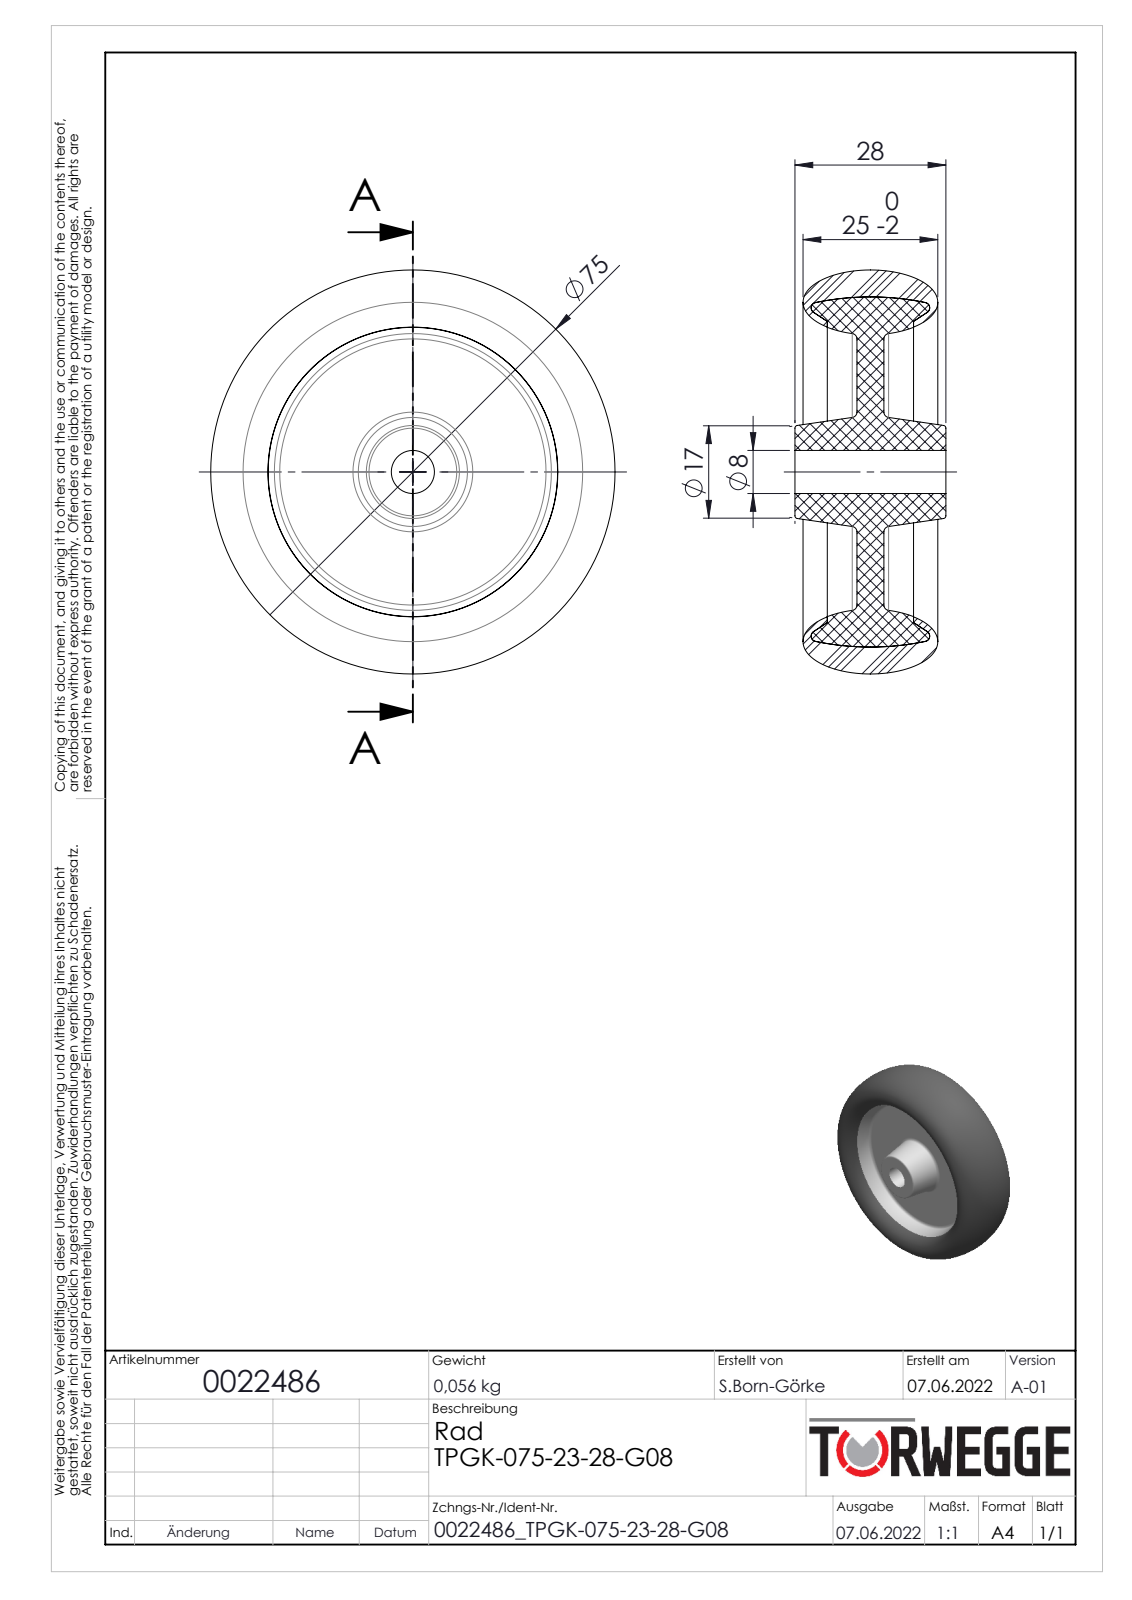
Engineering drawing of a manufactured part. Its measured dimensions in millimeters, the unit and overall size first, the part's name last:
Units: millimetres
Overall size (bounding box): 75 × 75 × 28
Round holes (diameter × count): ⌀8 ×1
Main face-to-face distances: 5, 5.5, 10.5, 16, 6, 11.5, 16.5, 22, 28
Volume: 62 012 mm³ · Surface area: 29 856 mm²
Bodies: 2 solids, 62 faces (8 planar, 2 cylindrical, 52 other)
Part name (STEP PRODUCT): 0022486
STEP written by: SolidWorks 2020 (AUTOMOTIVE_DESIGN)
